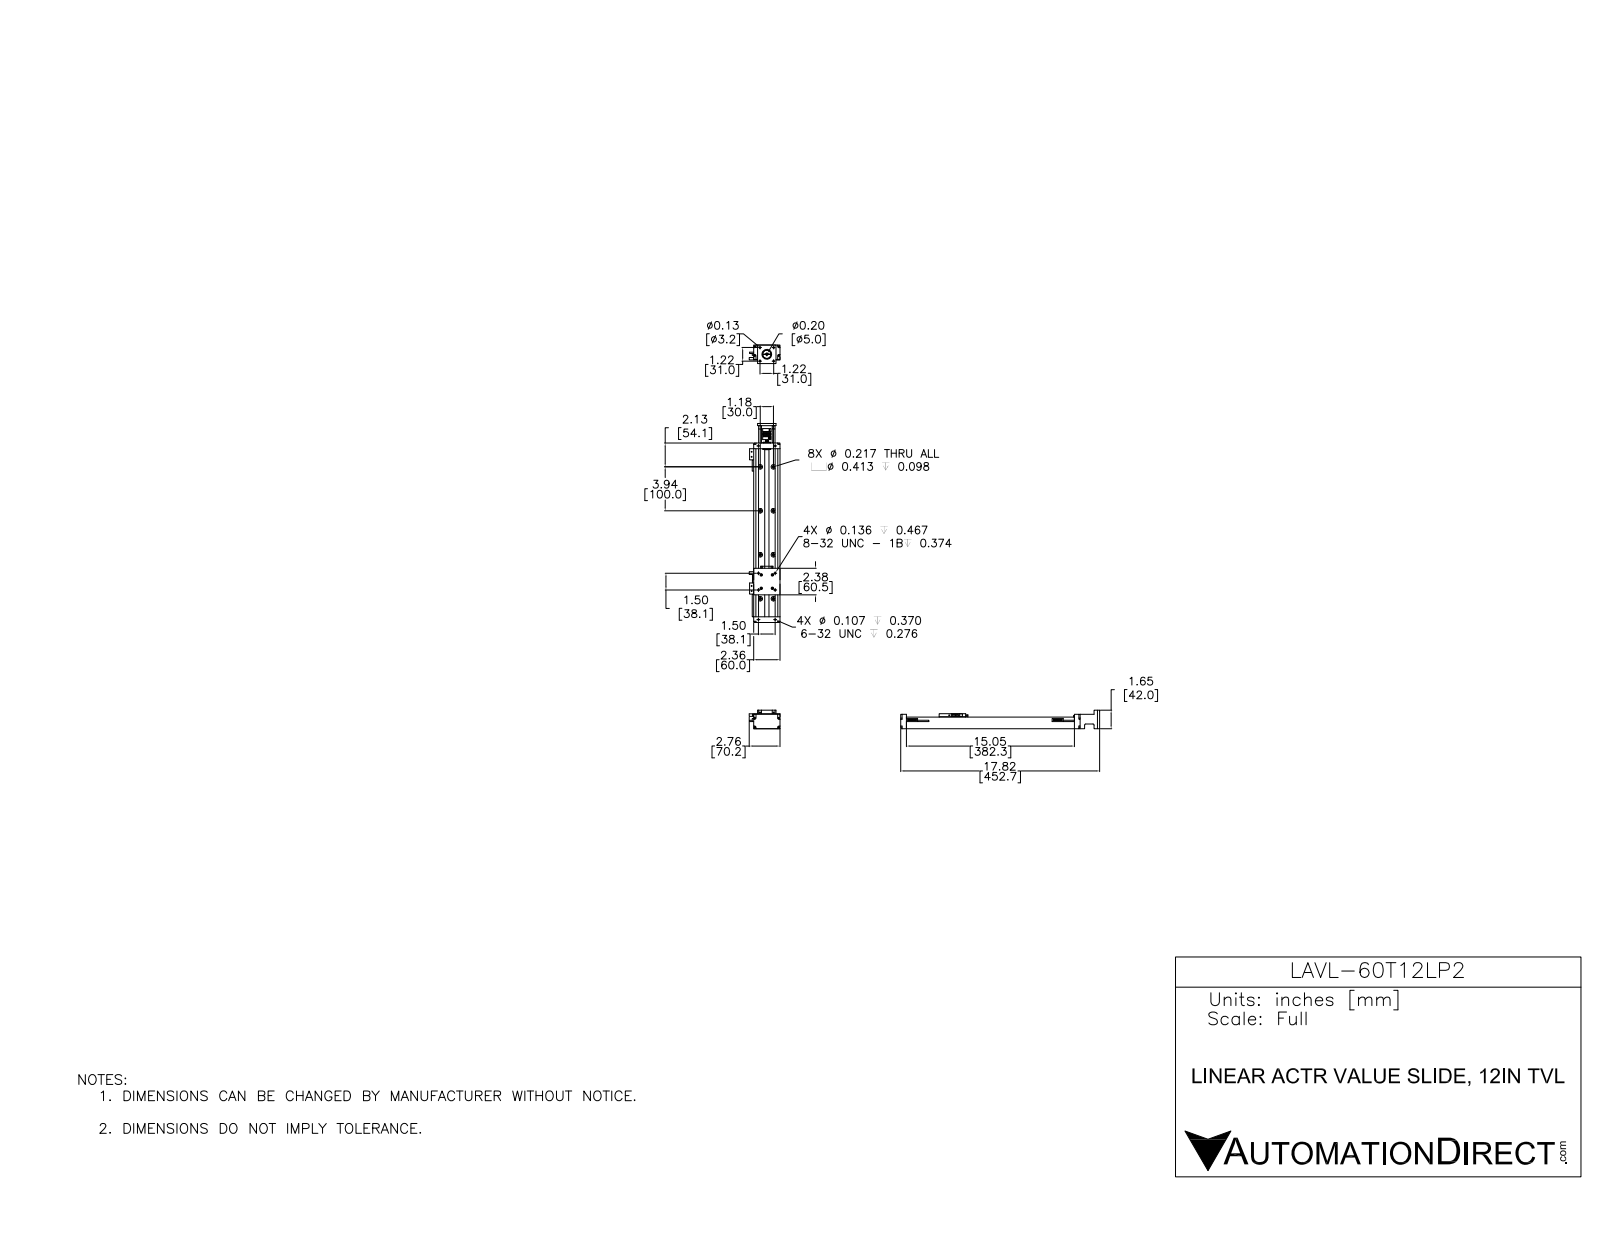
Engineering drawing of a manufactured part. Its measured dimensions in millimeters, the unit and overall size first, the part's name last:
Units: millimetres
Overall size (bounding box): 452.7 × 70.2 × 42
Round holes (diameter × count): ⌀3.3 ×12, ⌀2.7 ×10, ⌀5.5 ×8, ⌀10.5 ×8, ⌀2.3 ×6, ⌀3.5 ×6, ⌀2.2 ×4, ⌀3 ×4, ⌀3.2 ×4, ⌀3.2 ×4, ⌀3.8 ×4, ⌀5.6 ×4
Round bosses / shafts (diameter × count): ⌀5.6 ×4, ⌀5.3 ×4, ⌀4 ×2, ⌀19 ×1, ⌀17.5 ×1, ⌀17.1 ×1, ⌀15.9 ×1, ⌀12.9 ×1
Partial cylindrical surfaces — rounded edges, fillets, slot ends (radius × count): R2.8 ×8, R1.2 ×4, R5.4 ×4, R6.8 ×4, R1.2 ×3, R4.8 ×3, R1.4 ×2, R1.6 ×2
Main face-to-face distances: 5.1, 54.9, 60, 49.8, 11.3, 16.4, 26.5, 21.4, 10.1, 13
Hole centre spacings: 54.9, 27.7, 58.8, 31, 32.7, 38.1, 12.2, 12.9
Volume: 399 400 mm³ · Surface area: 188 700 mm²
Bodies: 19 solids, 887 faces (332 planar, 384 cylindrical, 171 other)
Part name (STEP PRODUCT): LAVL-60T06LP2-CAR; LAVL-60T12LP2-RAIL; LAVL-60T12LP2
STEP written by: SolidWorks 2015 (AUTOMOTIVE_DESIGN)
